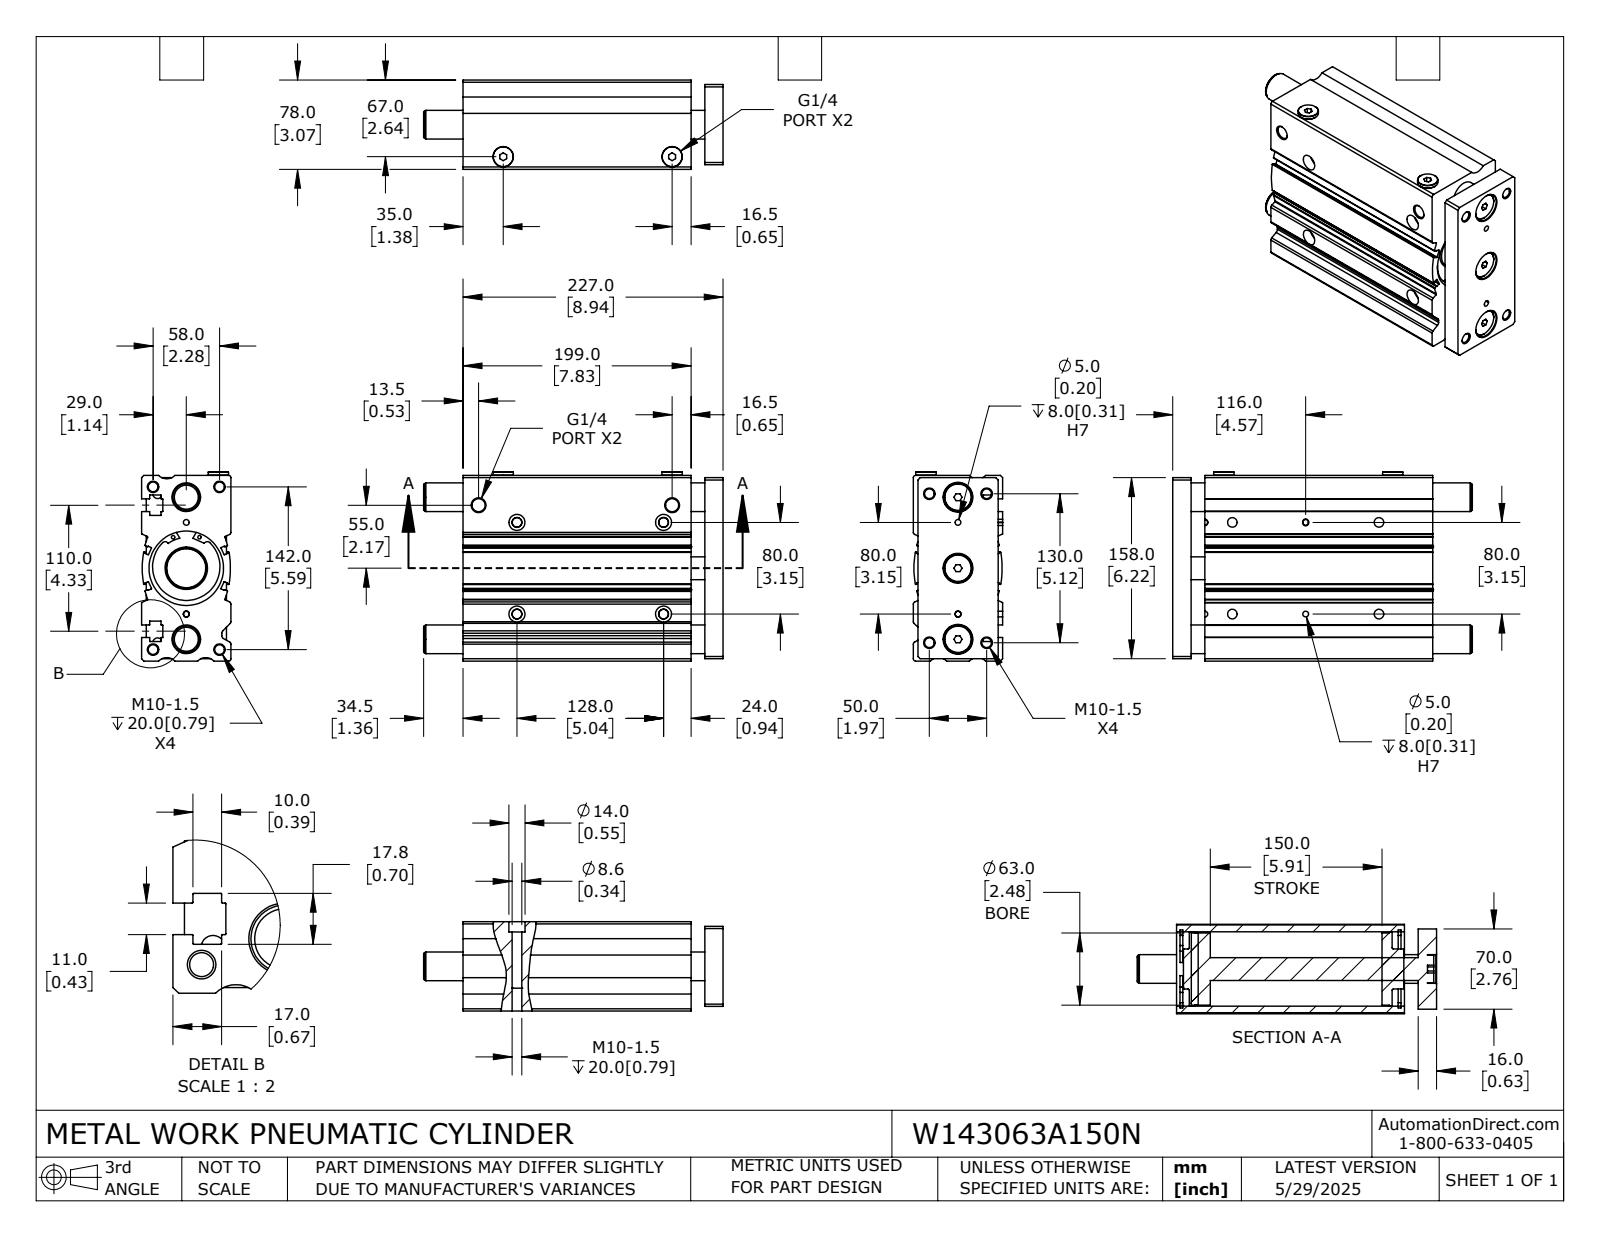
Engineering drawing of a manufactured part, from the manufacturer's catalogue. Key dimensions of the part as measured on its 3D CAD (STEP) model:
Part name (STEP PRODUCT): W143063A150N_ROD; W143063A150N_BODY; W143063A150N
STEP written by: SolidWorks 2024 (CONFIG_CONTROL_DESIGN)
Units: inches
Bodies: 6 solids, 465 faces (187 planar, 222 cylindrical, 56 other)
Overall size (bounding box): 10.295 × 6.496 × 3.071
Volume: 121.9 in³ · Surface area: 535.4 in²
Round holes (diameter × count): ⌀0.33 ×12, ⌀0.118 ×4, ⌀0.197 ×4, ⌀0.339 ×4, ⌀0.551 ×4, ⌀0.984 ×3, ⌀0.448 ×2, ⌀2.559 ×1
Round bosses / shafts (diameter × count): ⌀0.945 ×3, ⌀0.697 ×2, ⌀2.677 ×1, ⌀2.551 ×1, ⌀2.48 ×1, ⌀1.378 ×1, ⌀0.787 ×1
Partial cylindrical surfaces — rounded edges, fillets, slot ends (radius × count): R0.012 ×44, R0.02 ×12, R0.079 ×8, R0.098 ×8, R0.118 ×4, R0.394 ×3, R0.124 ×2, R1.157 ×2
Main face-to-face distances: 3.071, 0.63, 6.378, 0.472, 1.102, 8.937, 8.307, 7.835, 4.331, 0.728
Hole centre spacings: 0.284, 0.682, 0.991, 1.158, 1.195, 1.392, 1.448, 1.585
